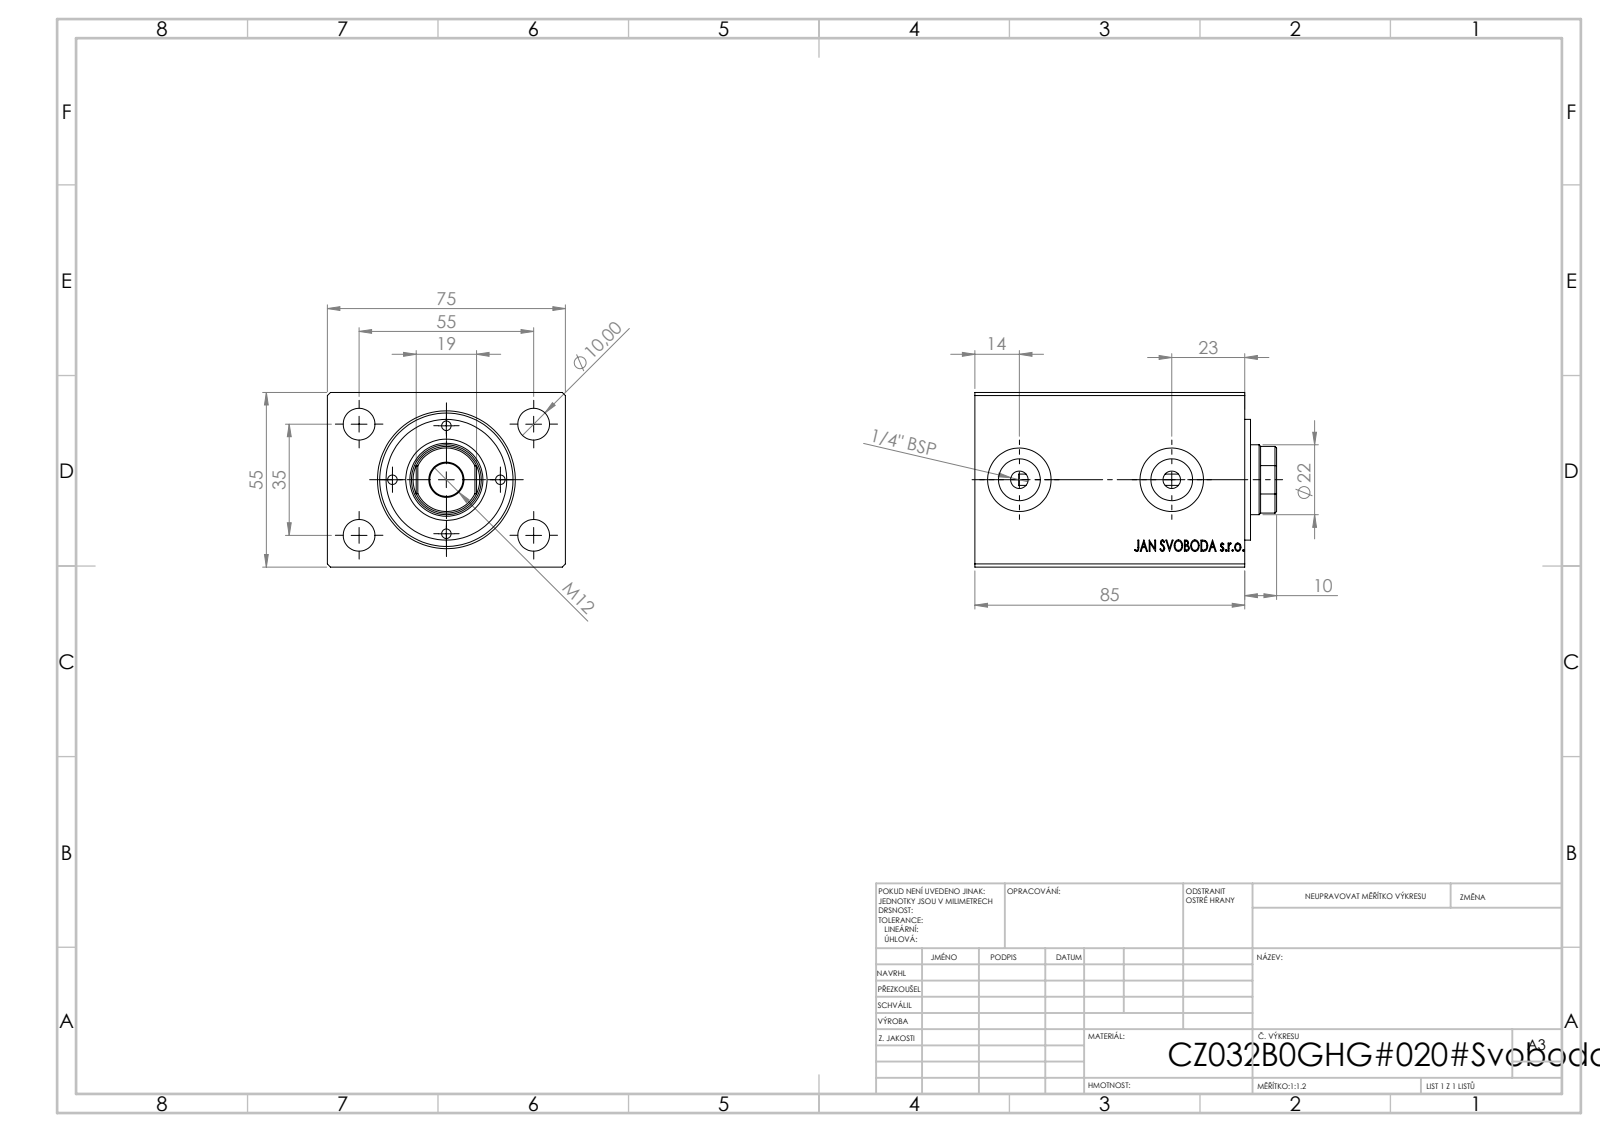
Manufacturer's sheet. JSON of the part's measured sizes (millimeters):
{"part_name": "V500CZ; V500CZ_B_VC", "step_written_by": "SolidWorks 2019 (CONFIG_CONTROL_DESIGN)", "units": "millimeters", "bodies": {"solids": 3, "faces": 875, "planar": 401, "cylindrical": 58, "other": 416}, "overall_size": [95, 75, 55], "volume_mm3": 323013, "surface_area_mm2": 58364, "round_holes": [[3, 4], [10, 4], [5.5, 2], [13.16, 2], [20, 2], [10.5, 1], [22, 1], [23, 1], [32, 1], [36, 1], [42, 1]], "round_bosses_or_shafts": [[38, 1]], "partial_cylinders_radius": [[10.5, 1]], "face_to_face_distances": [55, 75, 85, 71.2, 13.8, 10, 13.6, 8.2, 1.8, 84.8], "hole_center_spacings": [17, 20.41, 24.04, 27.5, 32.6, 44.12, 47.82, 34]}
